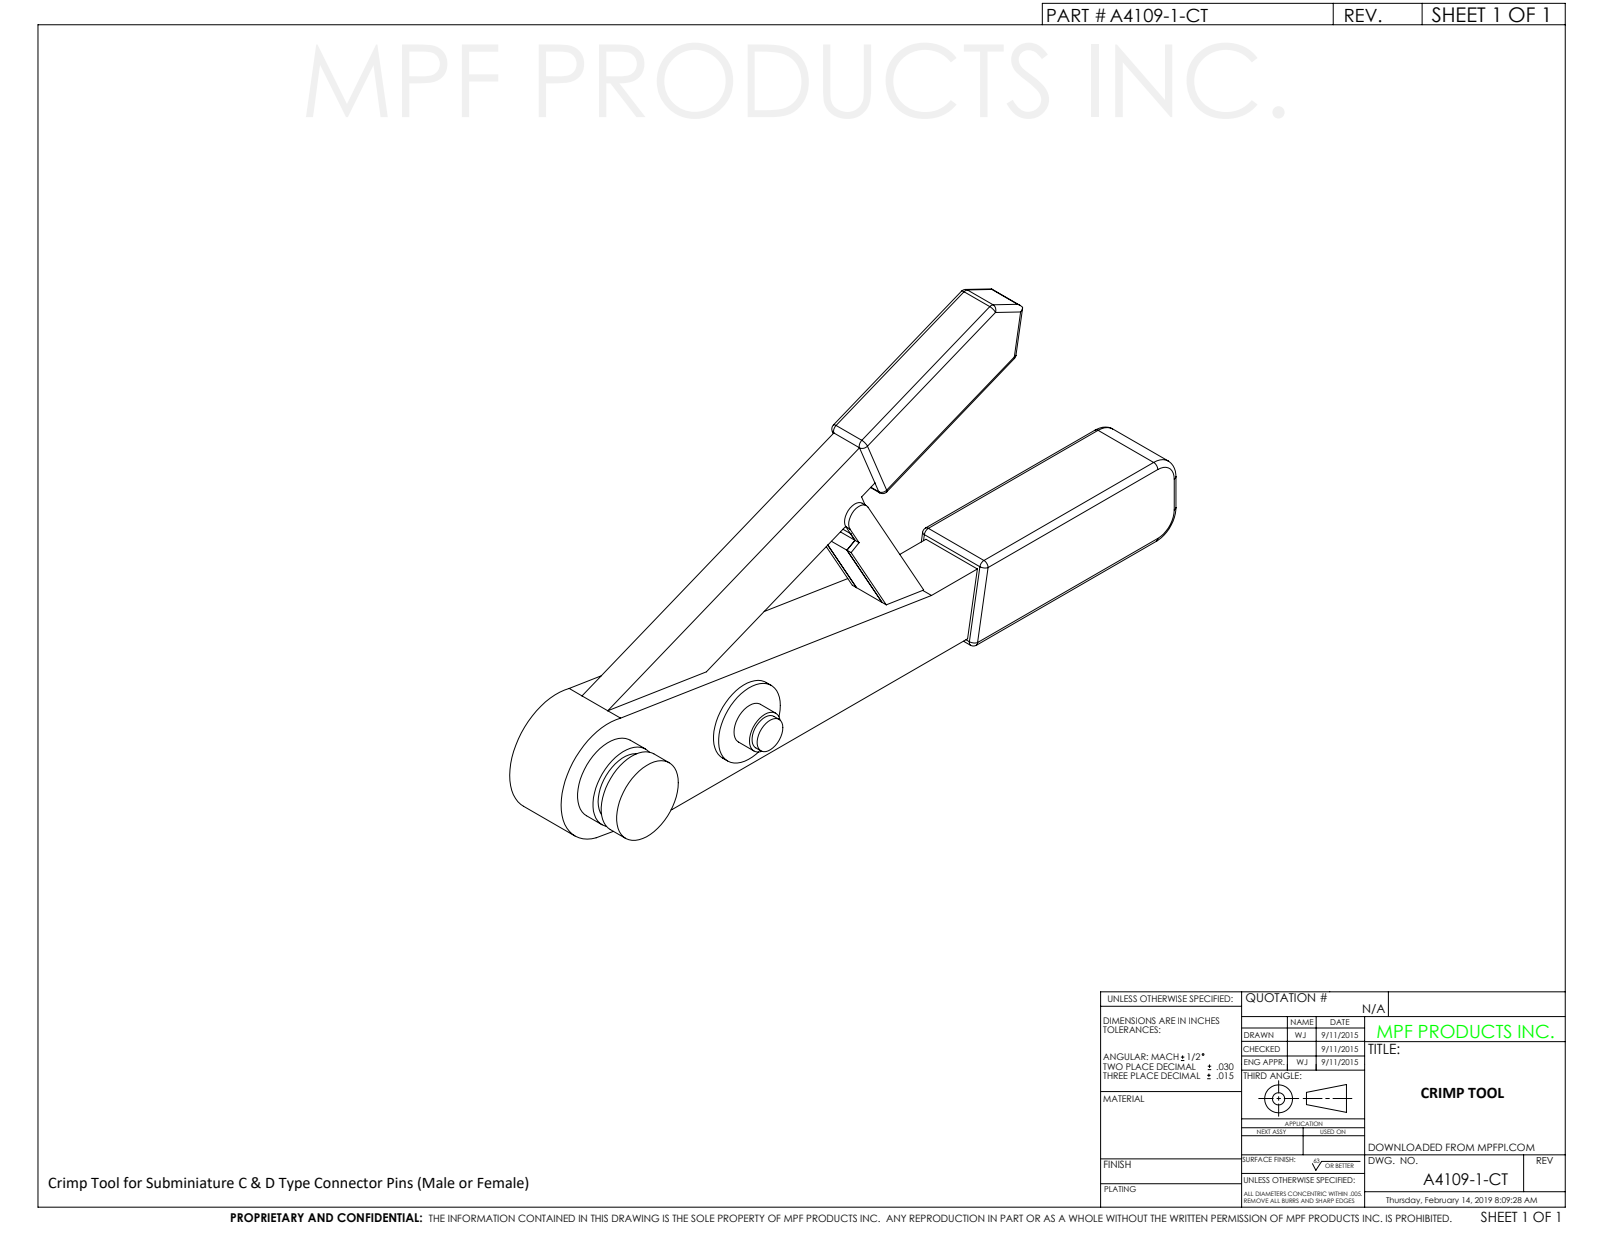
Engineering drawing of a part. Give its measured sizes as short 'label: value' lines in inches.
name: A4109-1-CT
written by: SolidWorks 2014 (CONFIG_CONTROL_DESIGN)
unit: in
bodies: 2 solids, 116 faces (52 planar, 46 cylindrical, 18 other)
size: 2.971 × 1.313 × 0.47
volume: 0.381 in³; area: 6.223 in²
bosses: 2× ⌀0.3, 1× ⌀0.25, 1× ⌀0.15, 1× ⌀0.125
rounds: 26× R0.02, 2× R0.1, 1× R0.05, 1× R0.23
face distances: 0.03, 0.187, 0.063, 0.25, 0.02, 0.093, 0.217, 0.28, 0.145, 0.072
